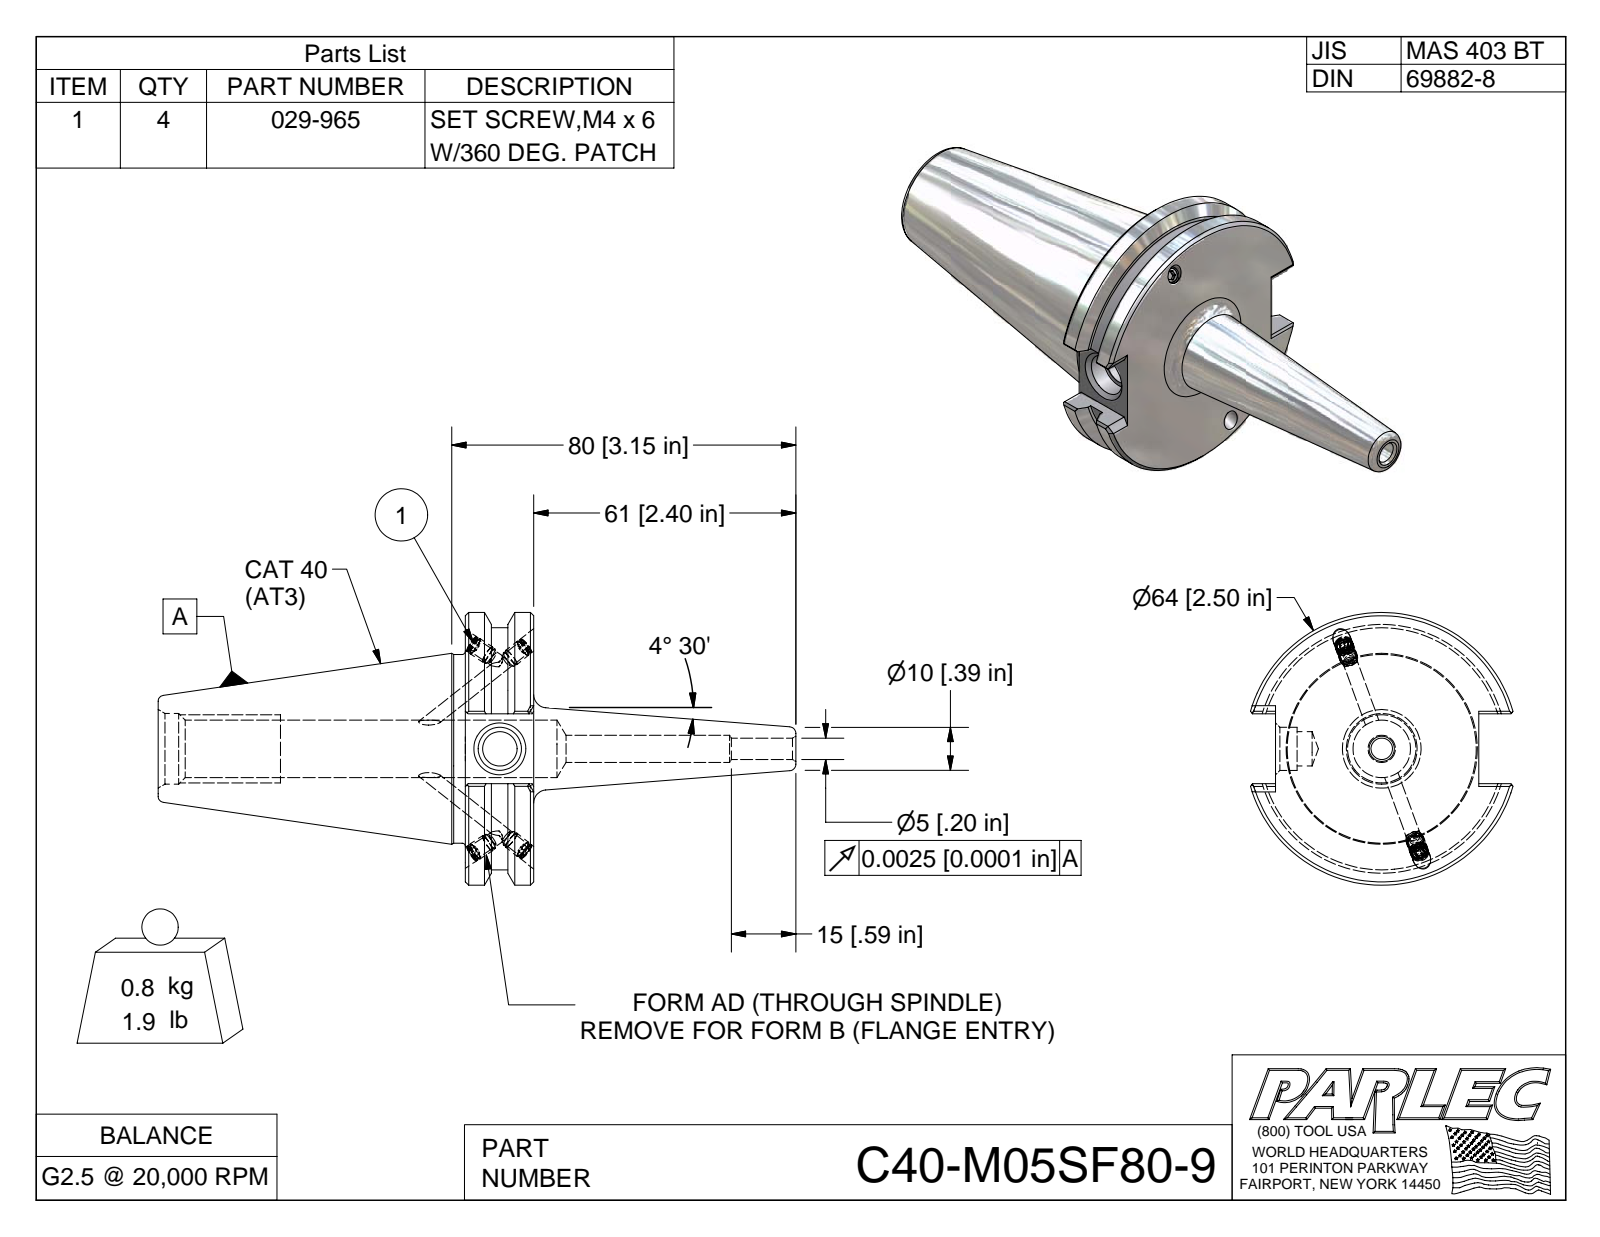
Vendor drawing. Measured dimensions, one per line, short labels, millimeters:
name: C40-M05SF80-9; C40BC-M05SF80-9-1; 029-965
written by: Autodesk Inventor 2009 (AUTOMOTIVE_DESIGN)
unit: mm
bodies: 5 solids, 148 faces (75 planar, 28 cylindrical, 45 other)
size: 148.3 × 63.5 × 61
volume: 108 400 mm³; area: 25 430 mm²
holes: 4× ⌀3.3, 4× ⌀4.1, 1× ⌀5
bosses: 4× ⌀4.2, 4× ⌀4, 1× ⌀63.5, 1× ⌀56.4, 1× ⌀43.9
face distances: 15.9, 16.3, 47.2, 71.4, 87.3, 81.3, 9.9, 6, 77.5, 6
